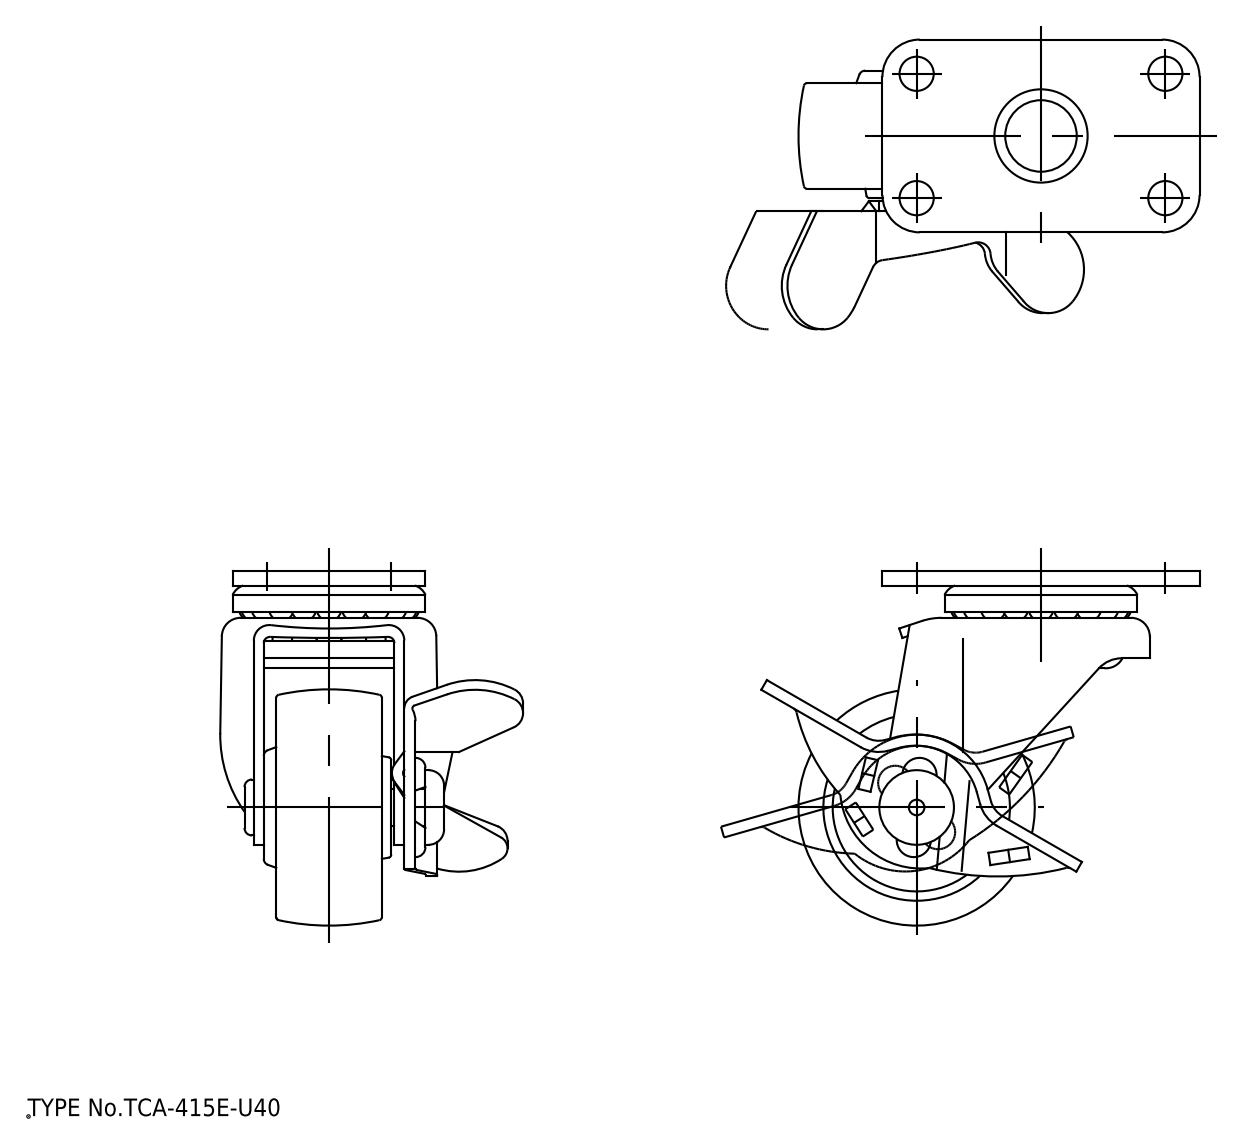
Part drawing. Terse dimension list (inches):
name: lever; mounting plate; main shaft; axle (+1 more)
written by: spGate 19.8.4 (****-****-****-****) (AUTOMOTIVE_DESIGN)
unit: in
bodies: 6 solids, 265 faces (86 planar, 83 cylindrical, 96 other)
size: 2.645 × 2.244 × 1.913
volume: 1.773 in³; area: 33.89 in²
holes: 4× ⌀0.217, 1× ⌀0.236, 1× ⌀0.24, 1× ⌀0.422, 1× ⌀0.453, 1× ⌀0.591
bosses: 1× ⌀1.22, 1× ⌀1.024
rounds: 10× R0.039, 5× R0.055, 4× R0.118, 4× R0.236, 3× R0.197, 2× R0.047, 2× R0.079, 2× R0.102
face distances: 0.063, 0.091, 0.89, 0.295, 0.594, 0.531, 0.358, 0.953, 0.217, 0.22
hole spacings: 0.88, 0.787, 1.575, 1.761
